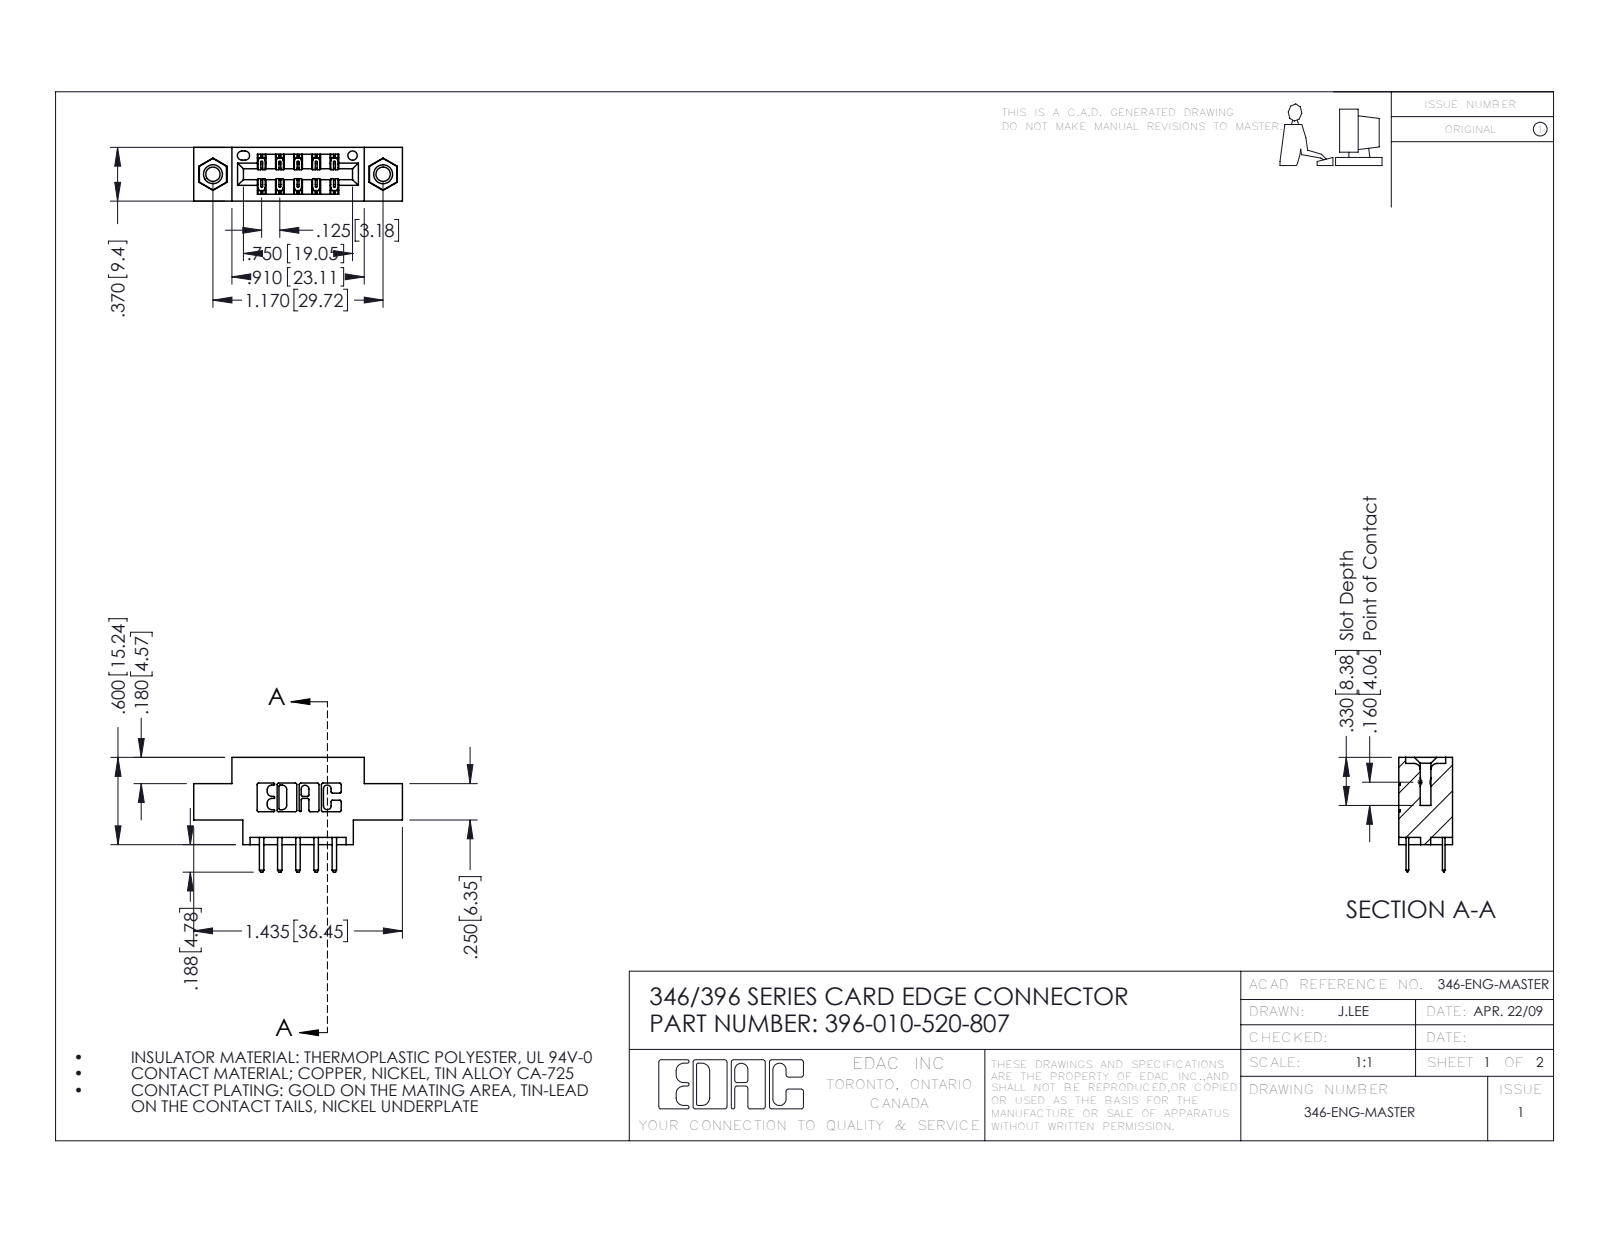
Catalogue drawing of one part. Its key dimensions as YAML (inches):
part_name: "396-010-520-807; 345-292-001_345-293-120; 346 Part_0.170 Offset - 0.156 Dia-TI; 345-250-001_345-250-005-103"
step_written_by: "SolidWorks 2016 (CONFIG_CONTROL_DESIGN)"
units: inches
bodies: {solids: 13, faces: 746, planar: 482, cylindrical: 248, other: 16}
overall_size: [1.435, 0.788, 0.37]
volume: 0.189
surface_area: 6.006
round_holes:
  - {diameter: 0.098, count: 2}
  - {diameter: 0.125, count: 2}
  - {diameter: 0.156, count: 2}
  - {diameter: 0.064, count: 1}
round_bosses_or_shafts:
  - {diameter: 0.155, count: 2}
partial_cylinders:
  - {radius: 0.01, count: 22}
  - {radius: 0.006, count: 15}
  - {radius: 0.01, count: 14}
  - {radius: 0.007, count: 6}
  - {radius: 0.031, count: 6}
  - {radius: 0.026, count: 3}
  - {radius: 0.014, count: 2}
  - {radius: 0.022, count: 2}
face_to_face_distances: [0.25, 0.37, 0.048, 0.322, 0.222, 0.148, 0.1, 0.174, 0.55, 0.072]
hole_center_spacings: [0.246, 0.969, 1.17]
